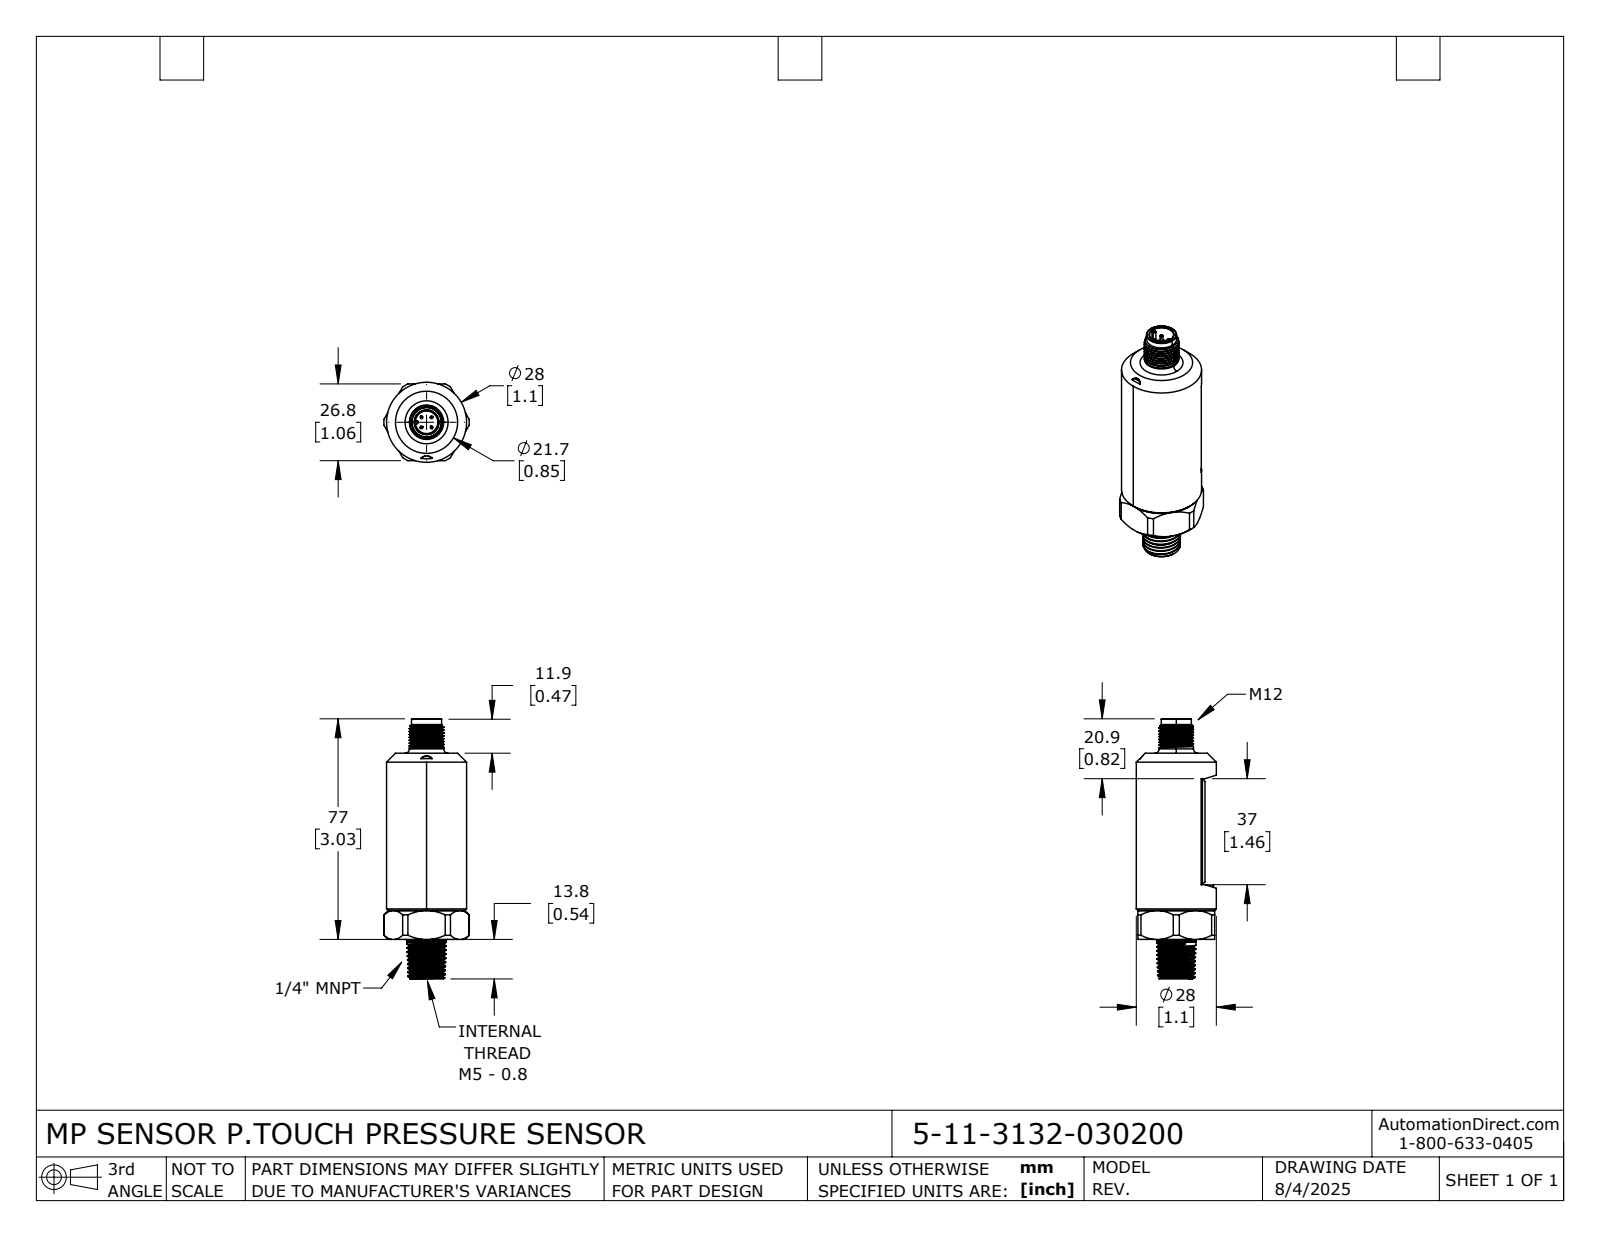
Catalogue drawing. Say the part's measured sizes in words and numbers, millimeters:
The part is named "5-11-3132-030200". Its 3-D file was written by "SolidWorks 2024 (AUTOMOTIVE_DESIGN)". It is 1 solid with 199 faces: 46 planar, 68 cylindrical and 85 other. Overall it measures 90.8 by 29.8 by 27.9 millimeters. Its volume is 39 710 cubic millimeters and its surface area 8 916 square millimeters. Round holes: 1 of diameter 2, 1 of diameter 4.2, 1 of diameter 8.4. Round bosses or shafts: 4 of diameter 1, 1 of diameter 27.9, 1 of diameter 26, 1 of diameter 13.7, 1 of diameter 12, 1 of diameter 10.5. Partial cylindrical surfaces (rounded edges, fillets, slot ends): 2 of radius 0.2, 1 of radius 2.3, 1 of radius 14.9. The main face-to-face distances are 26.8, 65, 23.4, 3.4, 13.8, 78.8, 9, 46, 8.9, 4.7.
